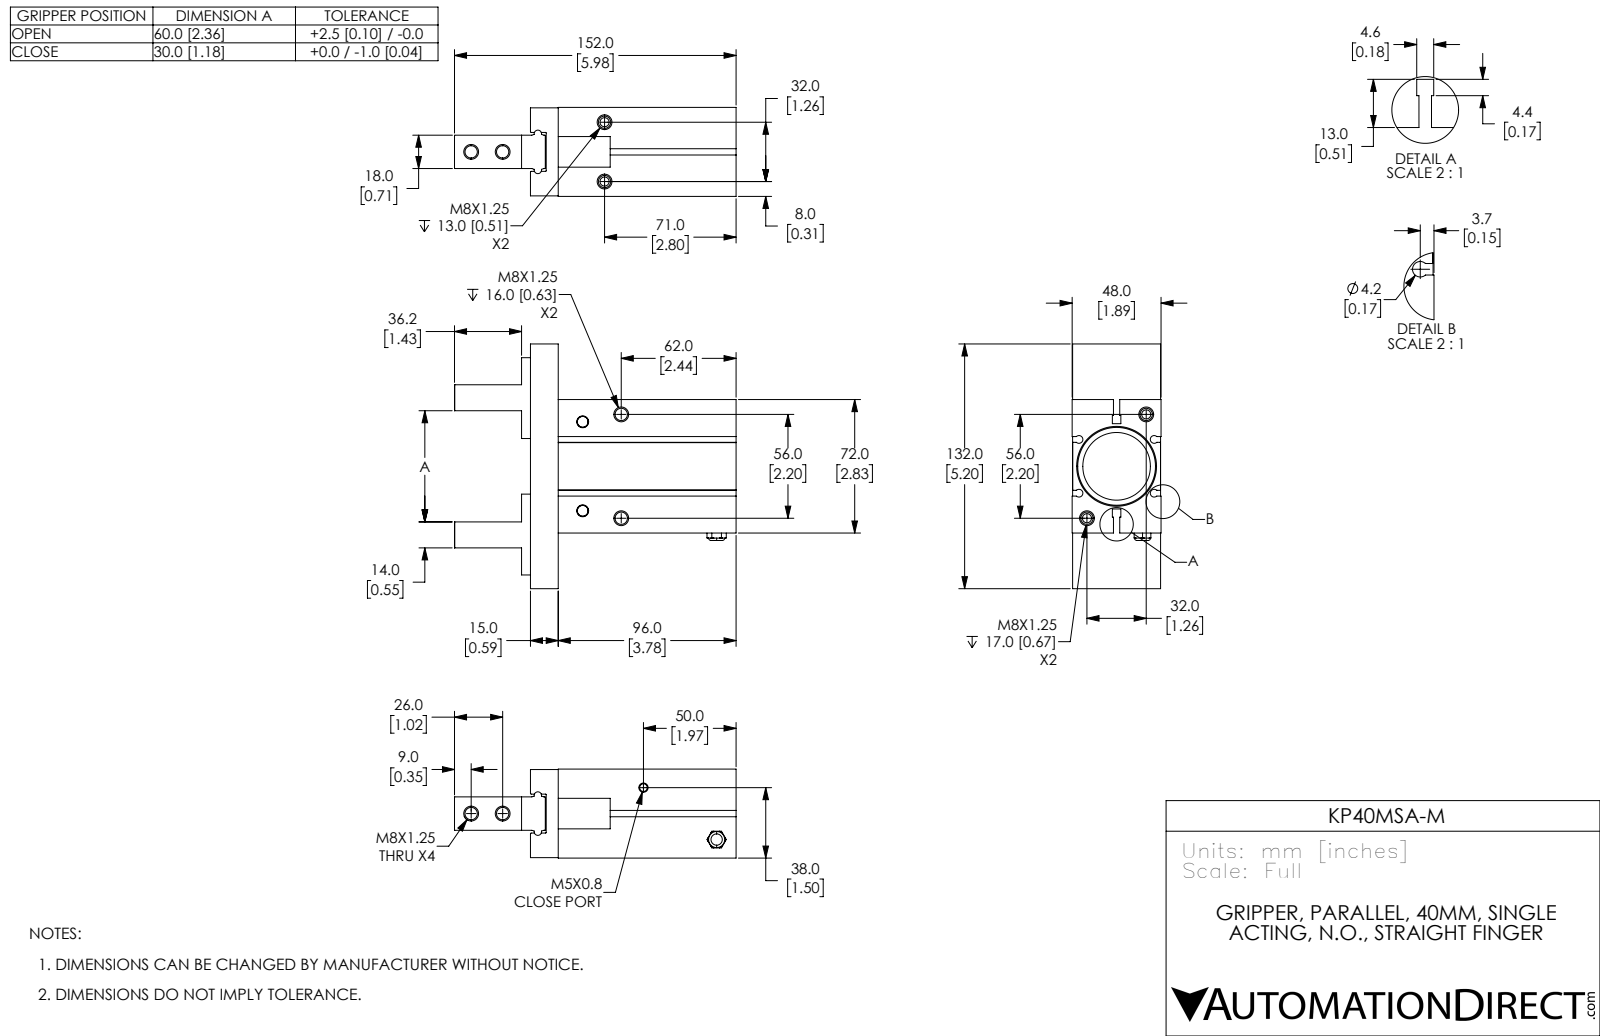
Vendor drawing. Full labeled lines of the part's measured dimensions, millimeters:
Part name (STEP PRODUCT): KP40MSA-M; KP40MSA-M-2; KP40MSA-M-3; KP40MSA-M-1
STEP written by: SolidWorks 2017 (CONFIG_CONTROL_DESIGN)
Units: millimetres
Bodies: 3 solids, 262 faces (127 planar, 65 cylindrical, 70 other)
Overall size (bounding box): 152 × 132 × 48
Volume: 379 081 mm³ · Surface area: 72 410 mm²
Round holes (diameter × count): ⌀6.65 ×5, ⌀6.65 ×3, ⌀0.5 ×2, ⌀4.13 ×2, ⌀8.02 ×2, ⌀6.1 ×1, ⌀36.5 ×1, ⌀42 ×1
Partial cylindrical surfaces — rounded edges, fillets, slot ends (radius × count): R0.2 ×7, R2.1 ×4, R0.3 ×2, R2 ×2
Main face-to-face distances: 15, 47.7, 15.75, 32.25, 15.45, 31.95, 47.75, 15.5, 32, 47.45
Hole centre spacings: 32.25, 57.28, 73.76, 17, 21.1, 32, 36.62, 48.42
